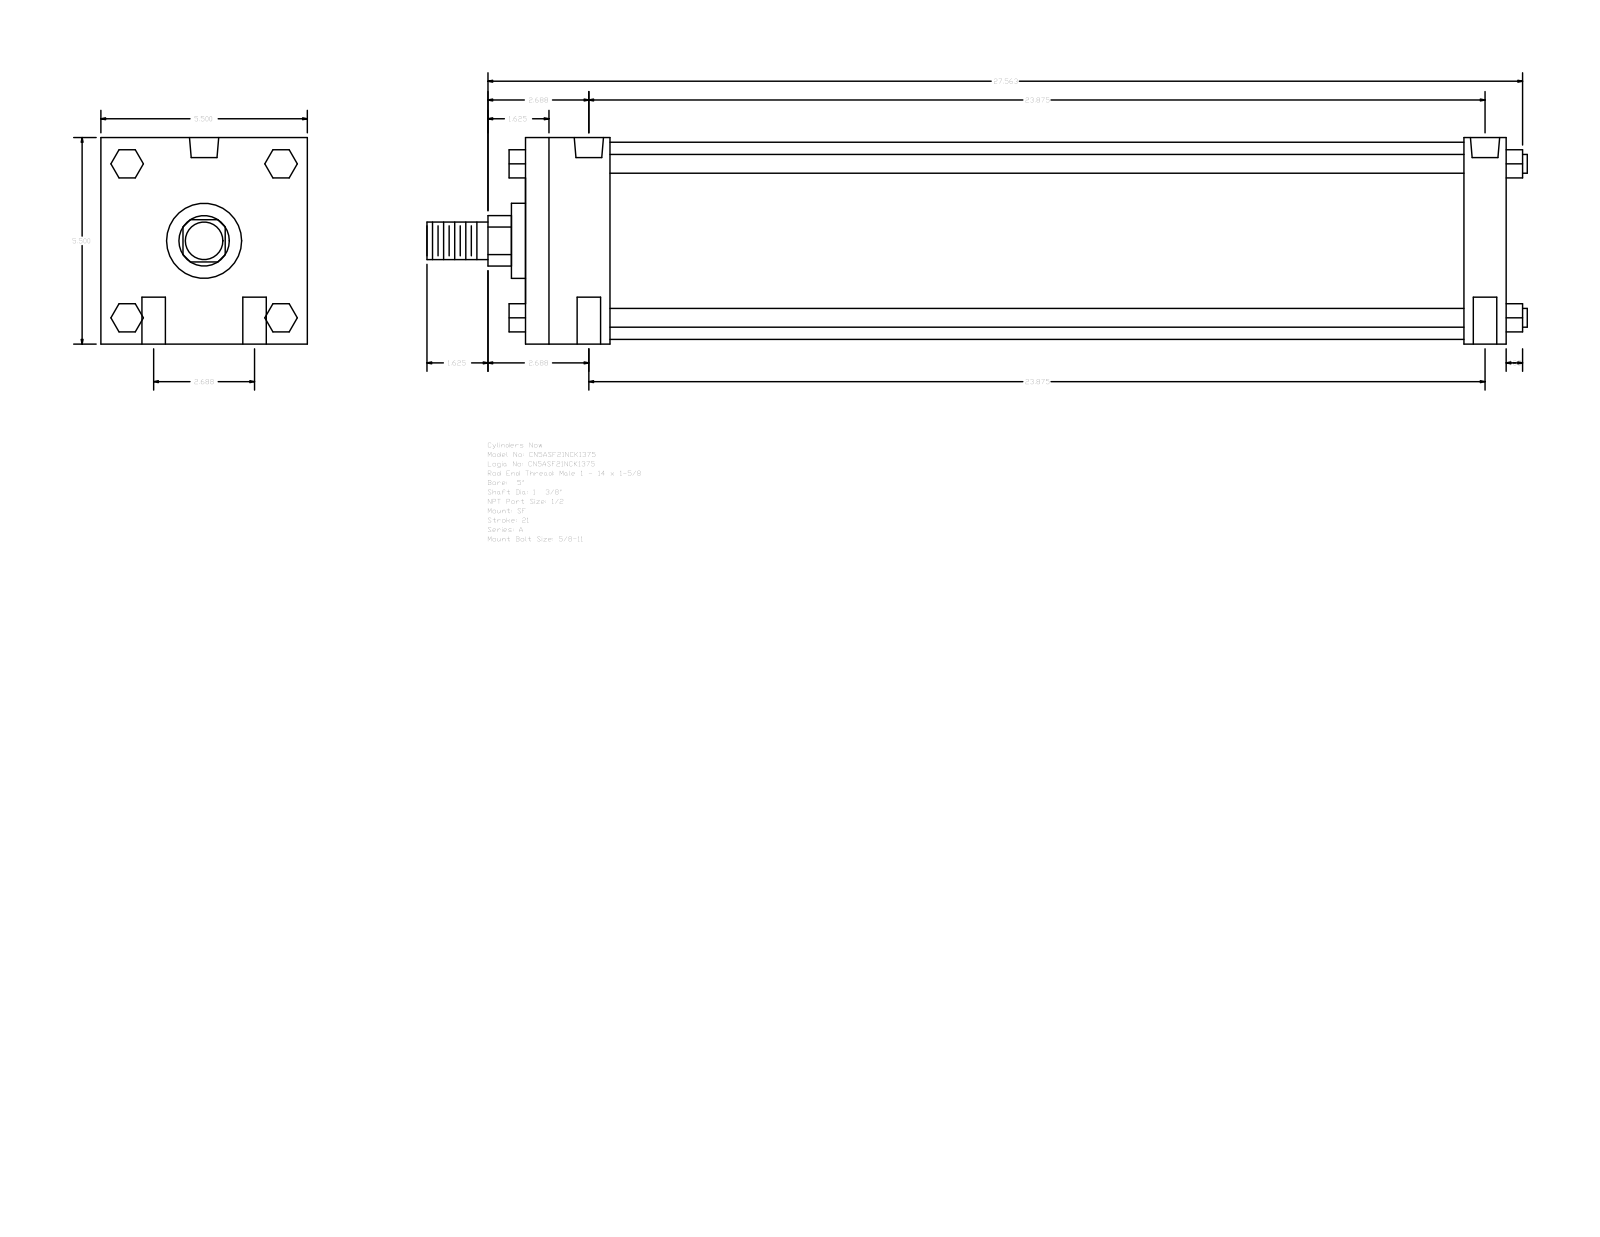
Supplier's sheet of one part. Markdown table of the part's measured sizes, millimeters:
| quantity | value |
| --- | --- |
| part name | A_SF__0500_1.375 |
| STEP written by | GSSL Pune (CONFIG_CONTROL_DESIGN) |
| units | millimeters |
| bodies | 0 solids, 124 faces (94 planar, 30 cylindrical, 0 other) |
| overall size | 744.54 × 139.7 × 139.7 |
| round holes (diameter × count) | 15.88 × 4, 8.73 × 2, 19.77 × 2 |
| round bosses / shafts (diameter × count) | 12.7 × 4, 133.35 × 1, 50.8 × 1, 34.92 × 1, 25.4 × 1 |
| partial cylindrical surfaces (radius × count) | 17.06 × 1 |
| main face-to-face distances | 139.7, 663.58, 57.15, 28.58, 635, 577.85, 606.43, 19.05, 52.07, 90.18 |
| hole center spacings | 34.13, 607.39, 606.43, 68.26, 610.26, 601.65 |
